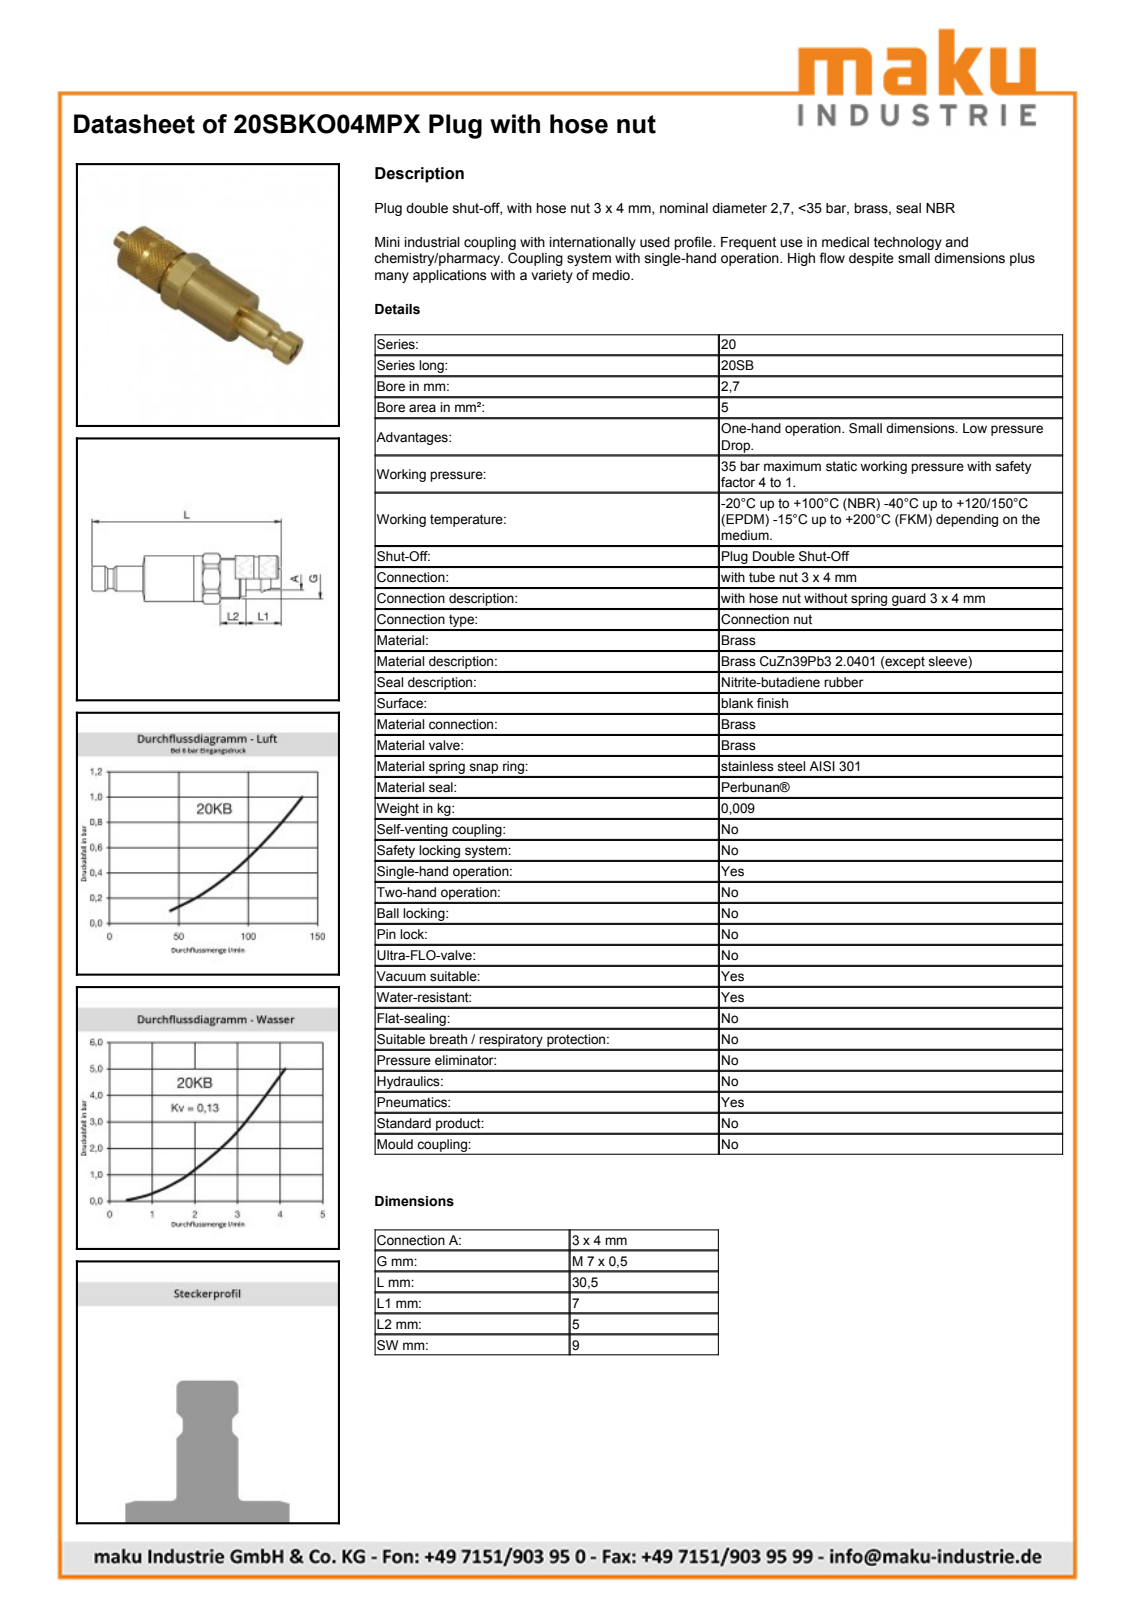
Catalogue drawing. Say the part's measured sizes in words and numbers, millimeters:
The part is named "D110518". Its 3-D file was written by "Autodesk Inventor 2013 (AUTOMOTIVE_DESIGN)". It is 1 solid with 72 faces: 18 planar, 22 cylindrical and 32 other. Overall it measures 35.55 by 9.78 by 9.74 millimeters. Its volume is 1 460 cubic millimeters and its surface area 1 255 square millimeters. Round holes: 1 of diameter 4.25, 1 of diameter 6.5, 1 of diameter 7.46. Round bosses or shafts: 1 of diameter 9, 1 of diameter 8.1, 1 of diameter 7.7, 1 of diameter 7.3, 1 of diameter 7, 1 of diameter 6.8, 1 of diameter 5, 1 of diameter 3.95. Partial cylindrical surfaces (rounded edges, fillets, slot ends): 1 of radius 4.95. The main face-to-face distances are 10, 9, 5, 13.55, 23.55, 3.55, 8.55, 20, 18.55, 15.05.
